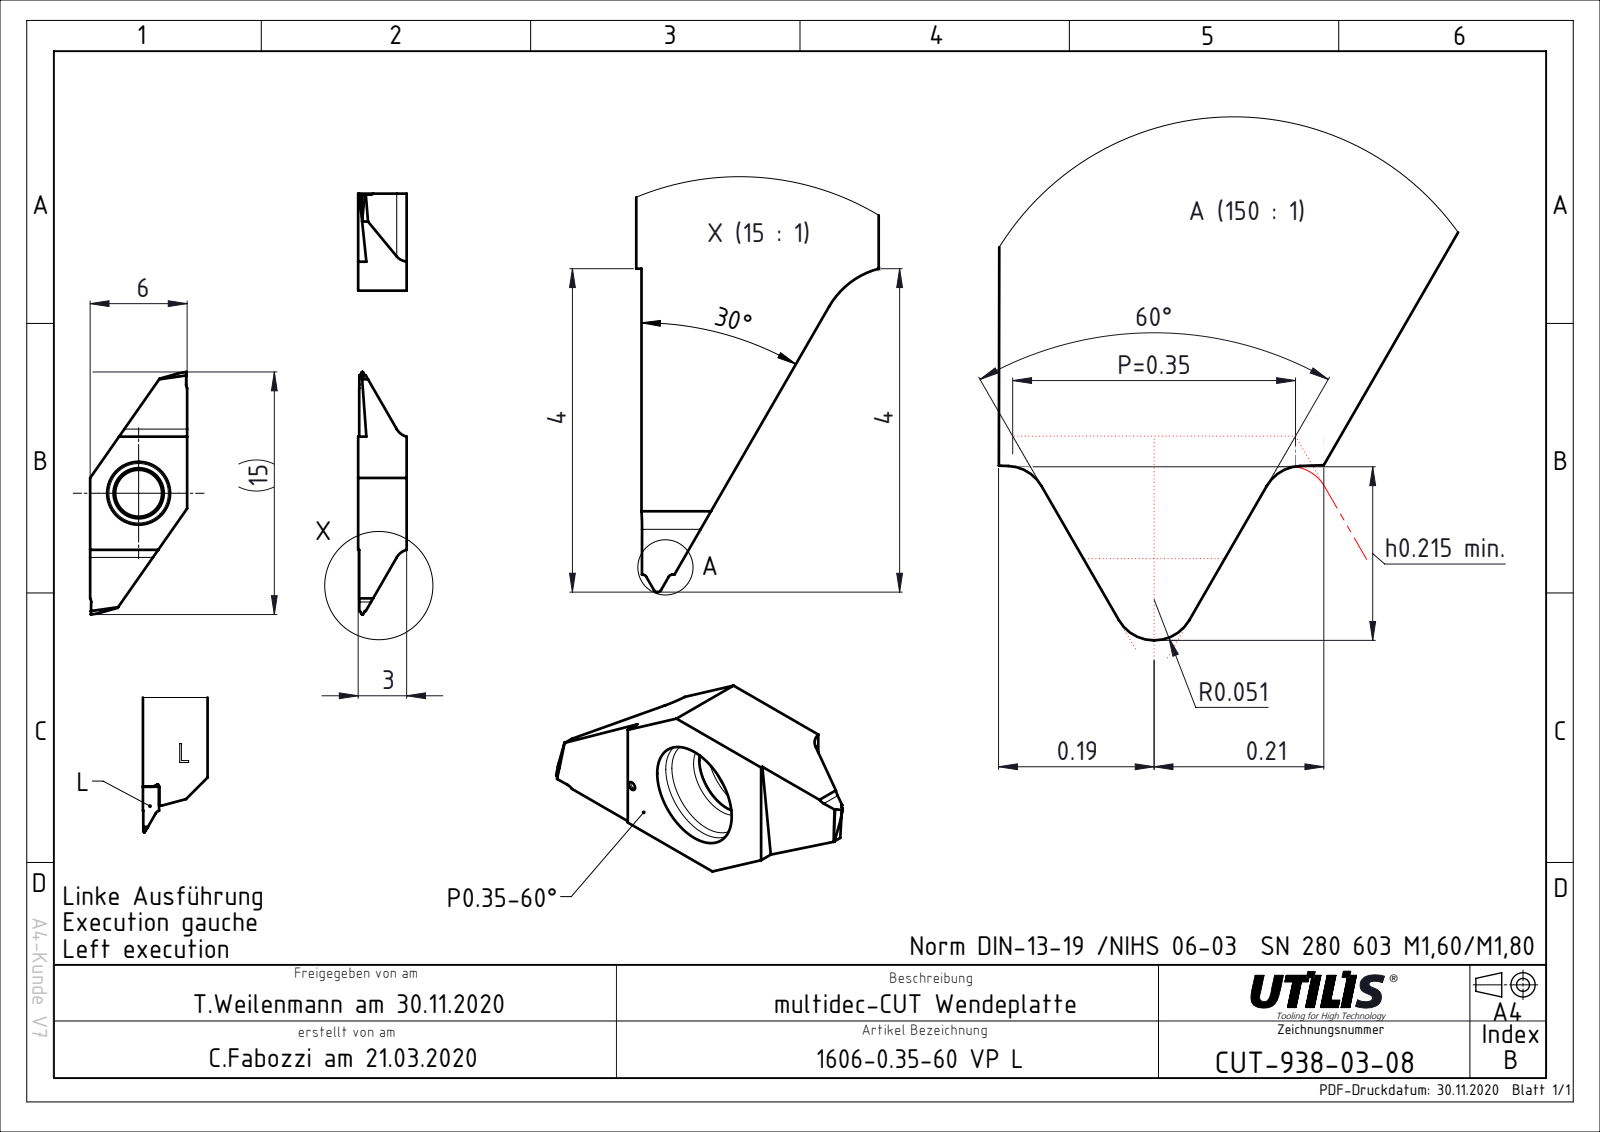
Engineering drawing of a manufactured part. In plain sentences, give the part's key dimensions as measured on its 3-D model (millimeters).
The part is named "CUT-938-03; ASME Y14.5". Its 3-D file was written by "FormatWorks Professional (AP242_MANAGED_MODEL_BASED_3D_ENGINEERING_MIM_LF)". It is 1 solid with 40 faces: 22 planar, 14 cylindrical and 4 other. Overall it measures 15 by 6 by 3 millimeters. Its volume is 129 cubic millimeters and its surface area 211 square millimeters. Round holes: 1 of diameter 2.9. Partial cylindrical surfaces (rounded edges, fillets, slot ends): 2 of radius 1. The main face-to-face distances are 6, 3, 9, 11.16, 12, 7, 13.09, 13.1.
